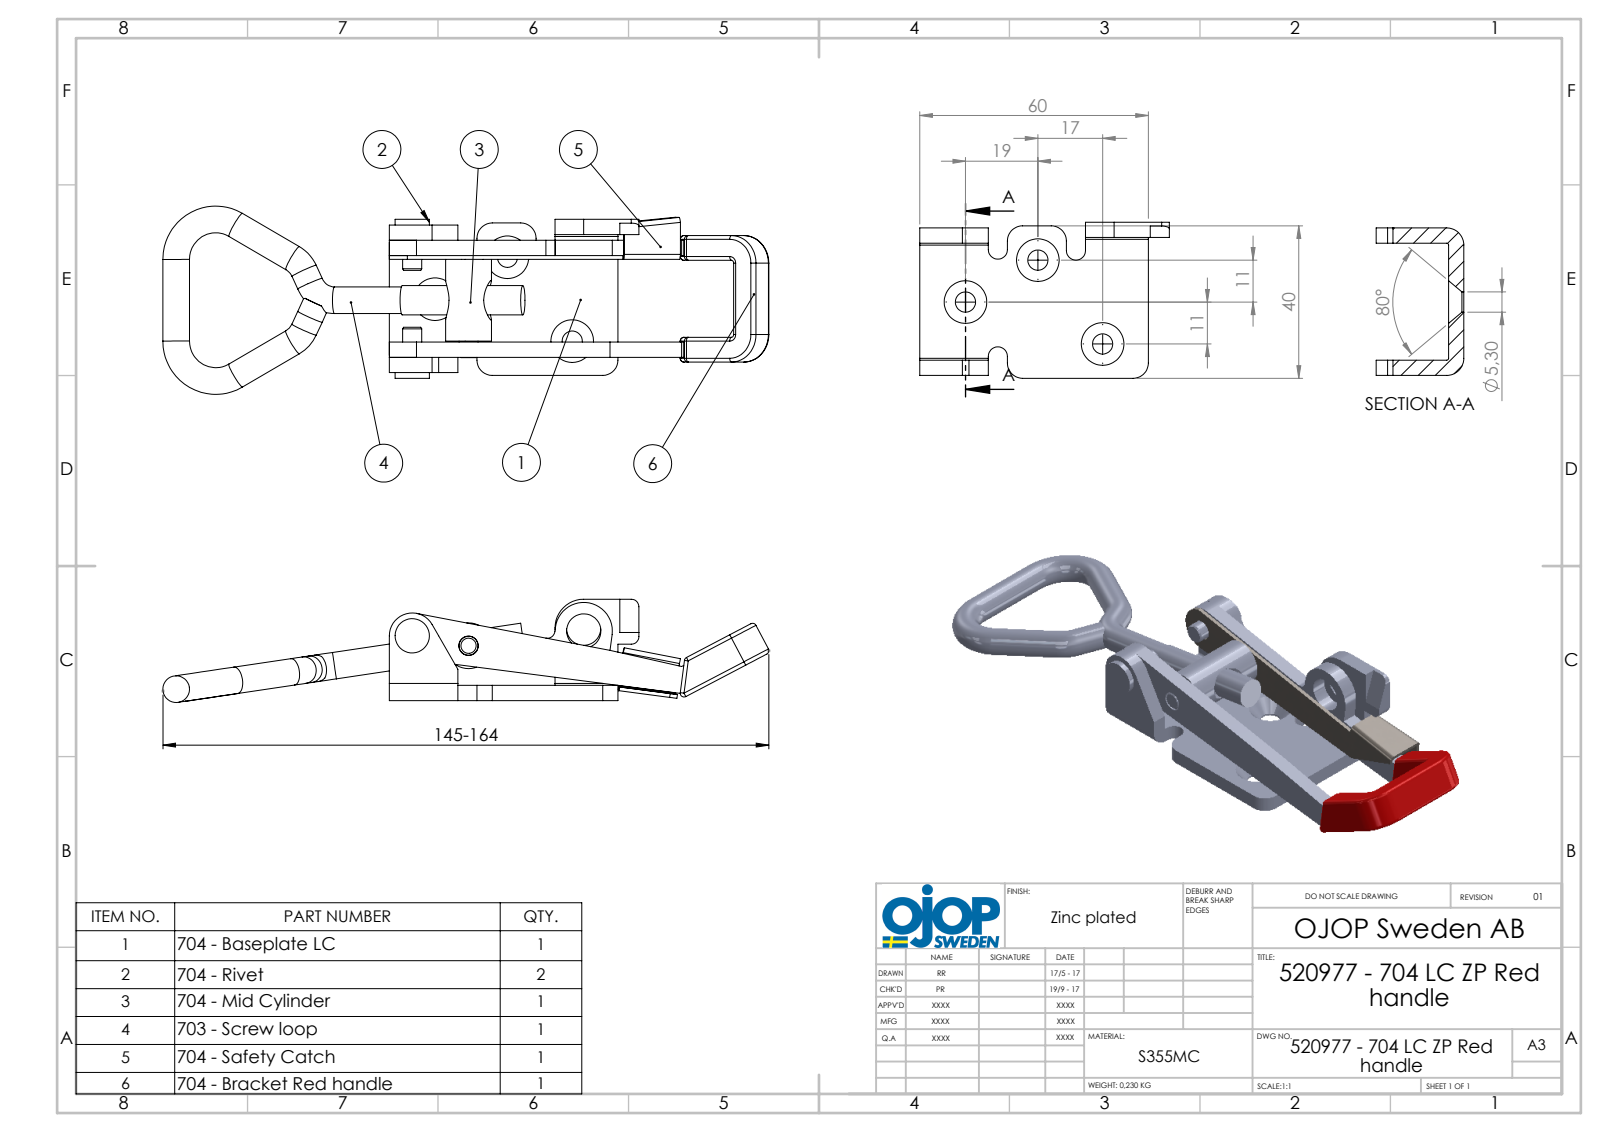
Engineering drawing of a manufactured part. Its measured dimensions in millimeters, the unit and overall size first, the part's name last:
Units: millimetres
Overall size (bounding box): 159.07 × 49.4 × 27.1
Round holes (diameter × count): ⌀5.3 ×3, ⌀5.1 ×2, ⌀9 ×2, ⌀5.4 ×1, ⌀7.2 ×1, ⌀7.7 ×1
Round bosses / shafts (diameter × count): ⌀7 ×4, ⌀5 ×2, ⌀12 ×1, ⌀9 ×1, ⌀7.7 ×1
Partial cylindrical surfaces — rounded edges, fillets, slot ends (radius × count): R1 ×18, R4 ×4, R0.3 ×3, R0.5 ×3, R1.3 ×3, R2 ×3, R2.5 ×3, R4.5 ×3
Main face-to-face distances: 4, 26.7, 30.7, 1, 5.5, 32.2, 5, 25.7, 36.2, 22.7
Hole centre spacings: 0.74, 15.02, 21.95, 27.8, 30.49, 30.56, 37.64, 45.04
Volume: 32 096 mm³ · Surface area: 22 676 mm²
Bodies: 7 solids, 272 faces (103 planar, 115 cylindrical, 54 other)
Part name (STEP PRODUCT): 704 - Rivet Gradin; 704 - Safety Catch; 703 - Skruvögla; 520977 - 704 LC ZP Red handle (+3 more)
STEP written by: SolidWorks 2015 (AUTOMOTIVE_DESIGN)
